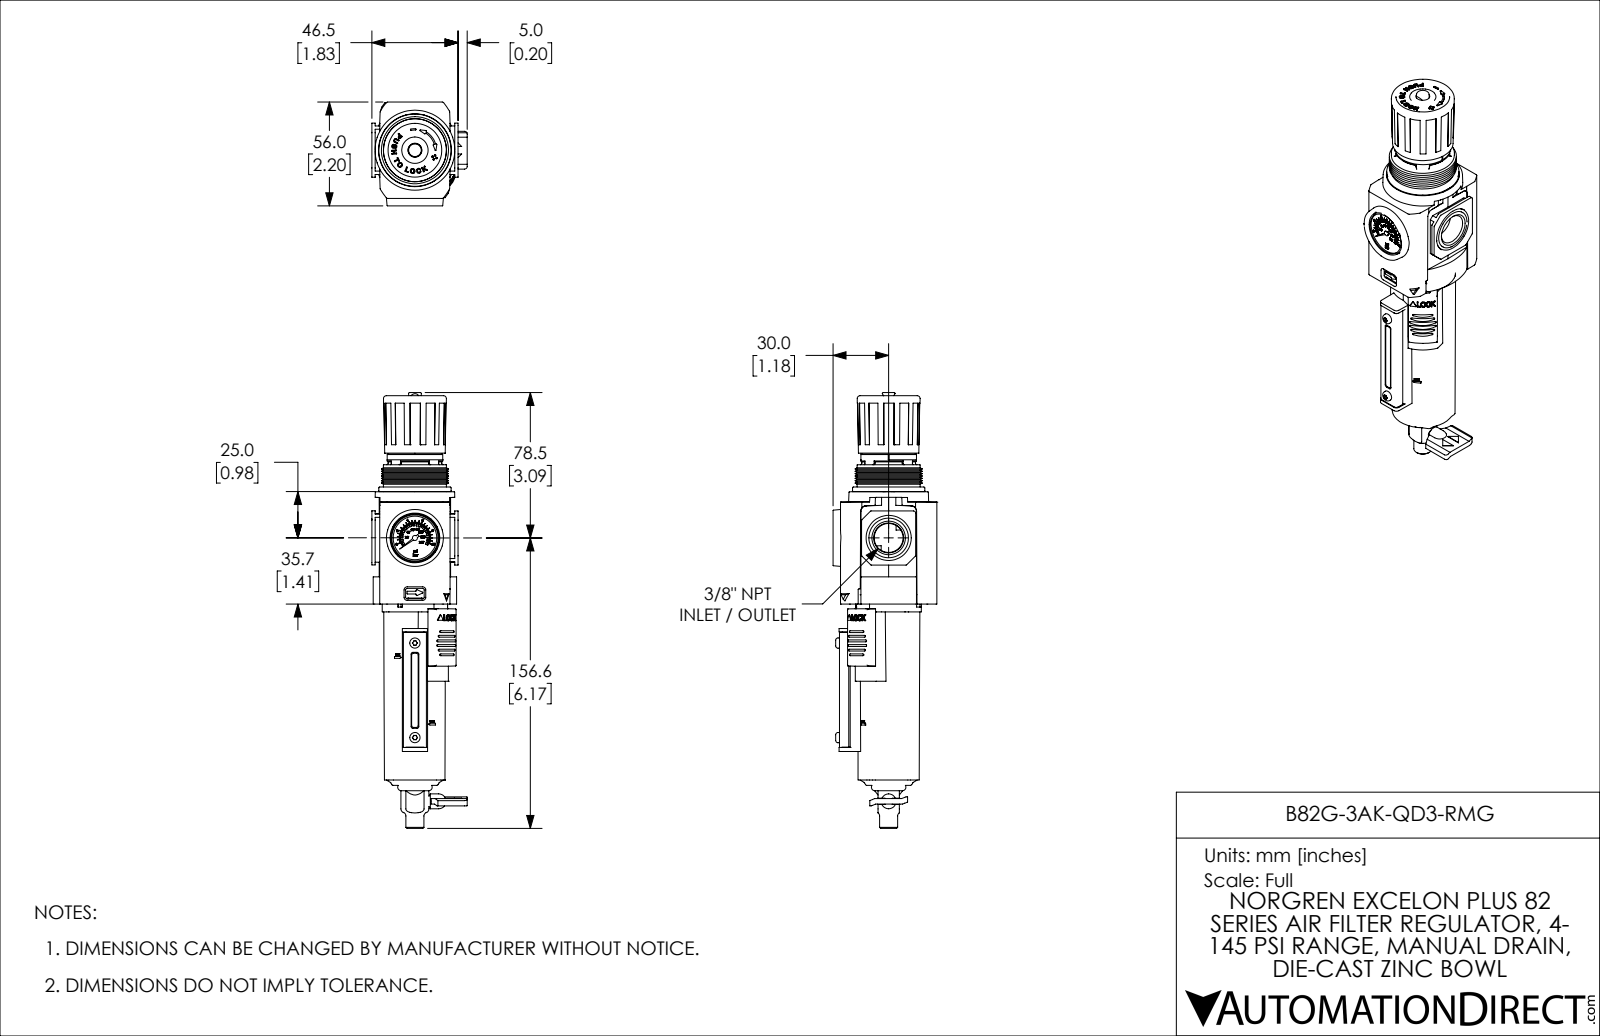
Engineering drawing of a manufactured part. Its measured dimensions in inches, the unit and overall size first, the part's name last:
Units: inches
Overall size (bounding box): 9.257 × 2.205 × 2.027
Round holes (diameter × count): ⌀0.097 ×4, ⌀0.138 ×2, ⌀0.128 ×1, ⌀0.197 ×1, ⌀0.236 ×1, ⌀0.25 ×1, ⌀0.628 ×1, ⌀0.925 ×1, ⌀1.102 ×1, ⌀1.354 ×1
Round bosses / shafts (diameter × count): ⌀0.224 ×2, ⌀0.217 ×2, ⌀0.118 ×2, ⌀1.535 ×1, ⌀1.388 ×1, ⌀1.356 ×1, ⌀1.339 ×1, ⌀1.291 ×1
Partial cylindrical surfaces — rounded edges, fillets, slot ends (radius × count): R0.02 ×50, R0.039 ×38, R0.009 ×25, R0.031 ×20, R0.006 ×19, R0.011 ×13, R0.012 ×12, R0.012 ×12
Main face-to-face distances: 0.059, 1.988, 1.693, 0.354, 1.634, 0.295, 1.417, 1.475, 0.236, 0.182
Hole centre spacings: 0.63, 1.091, 1.26, 2.705, 3.325, 2.965
Volume: 17 in³ · Surface area: 117.1 in²
Bodies: 8 solids, 2663 faces (1028 planar, 1243 cylindrical, 392 other)
Part name (STEP PRODUCT): B82G-3AK-QD3-RMG
STEP written by: SolidWorks 2021 (CONFIG_CONTROL_DESIGN)
